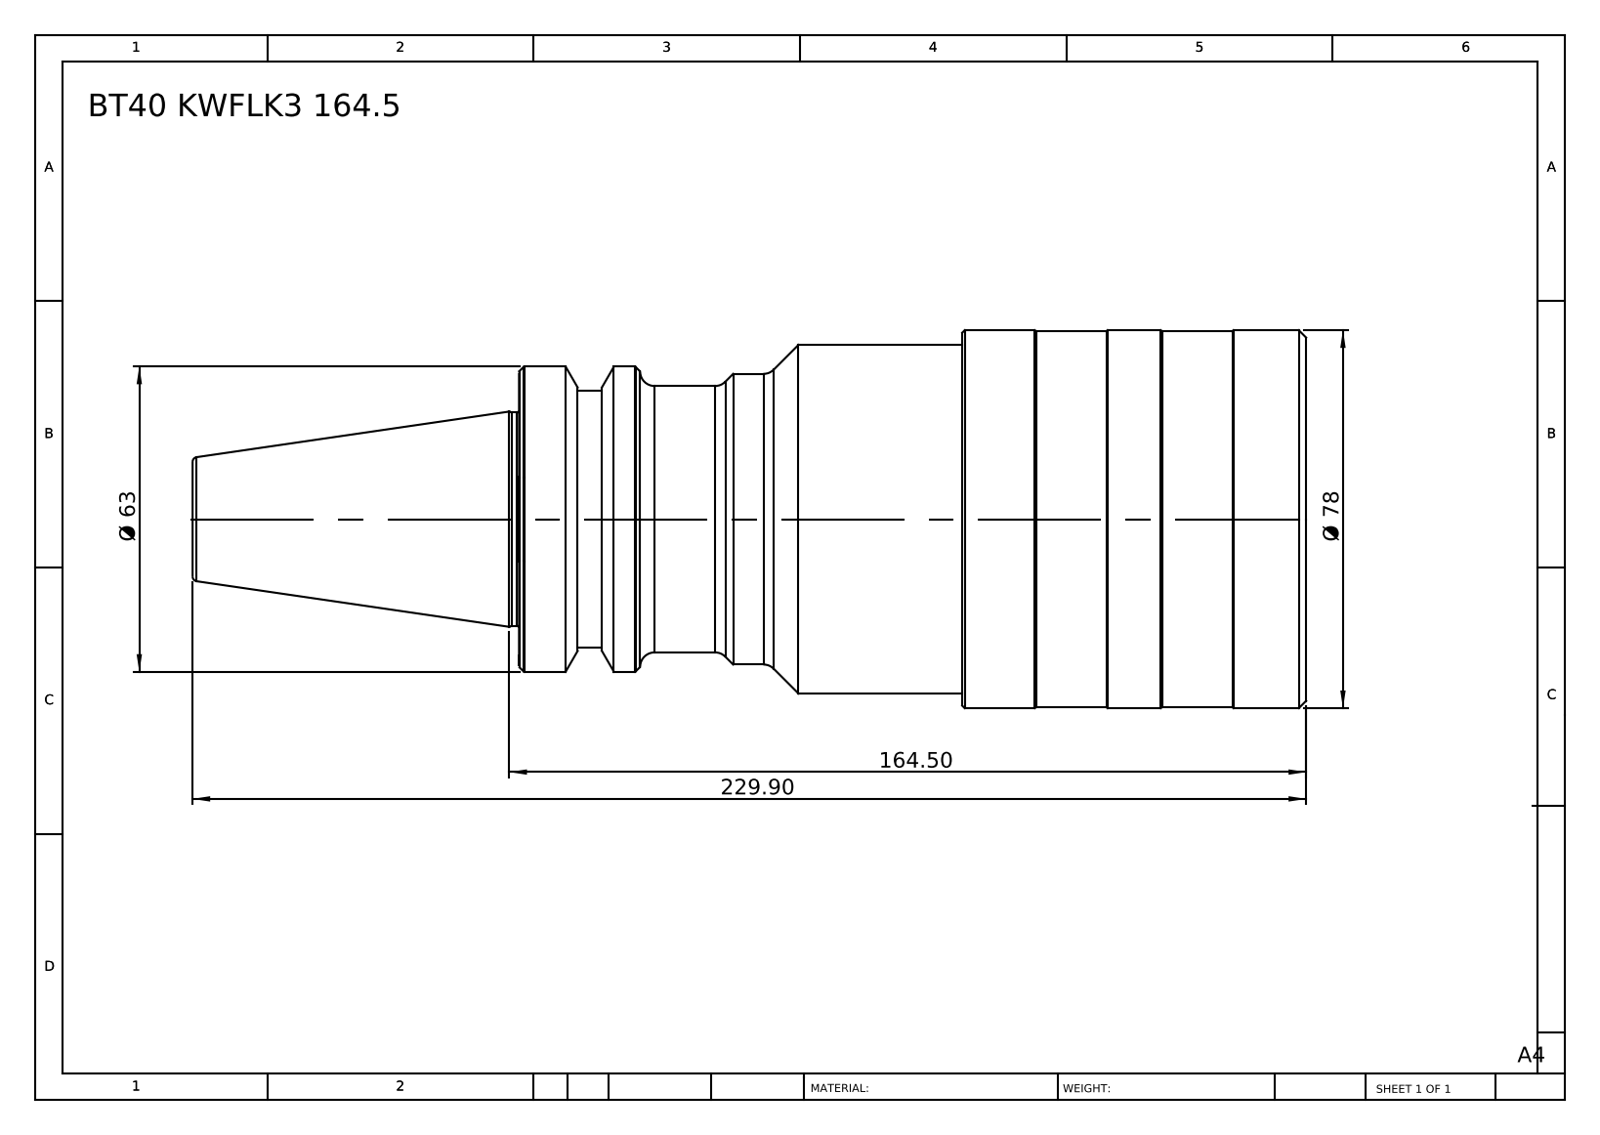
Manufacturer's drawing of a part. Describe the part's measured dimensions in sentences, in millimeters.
The part is named "BT40 KWFLK3 164.5". Its 3-D file was written by "SolidWorks 2014 (CONFIG_CONTROL_DESIGN)". It is 1 solid with 82 faces: 6 planar, 24 cylindrical and 52 other. Overall it measures 229.9 by 78 by 78 millimeters. Its volume is 701 528 cubic millimeters and its surface area 52 684 square millimeters. Round bosses or shafts: 1 of diameter 78, 1 of diameter 77.5, 1 of diameter 72, 1 of diameter 63, 1 of diameter 60, 1 of diameter 55, 1 of diameter 53, 1 of diameter 44. The main face-to-face distances are 162.5, 71, 91.5, 229.9, 158.9, 67.4, 150.4, 79.4, 12.1, 79.5.
